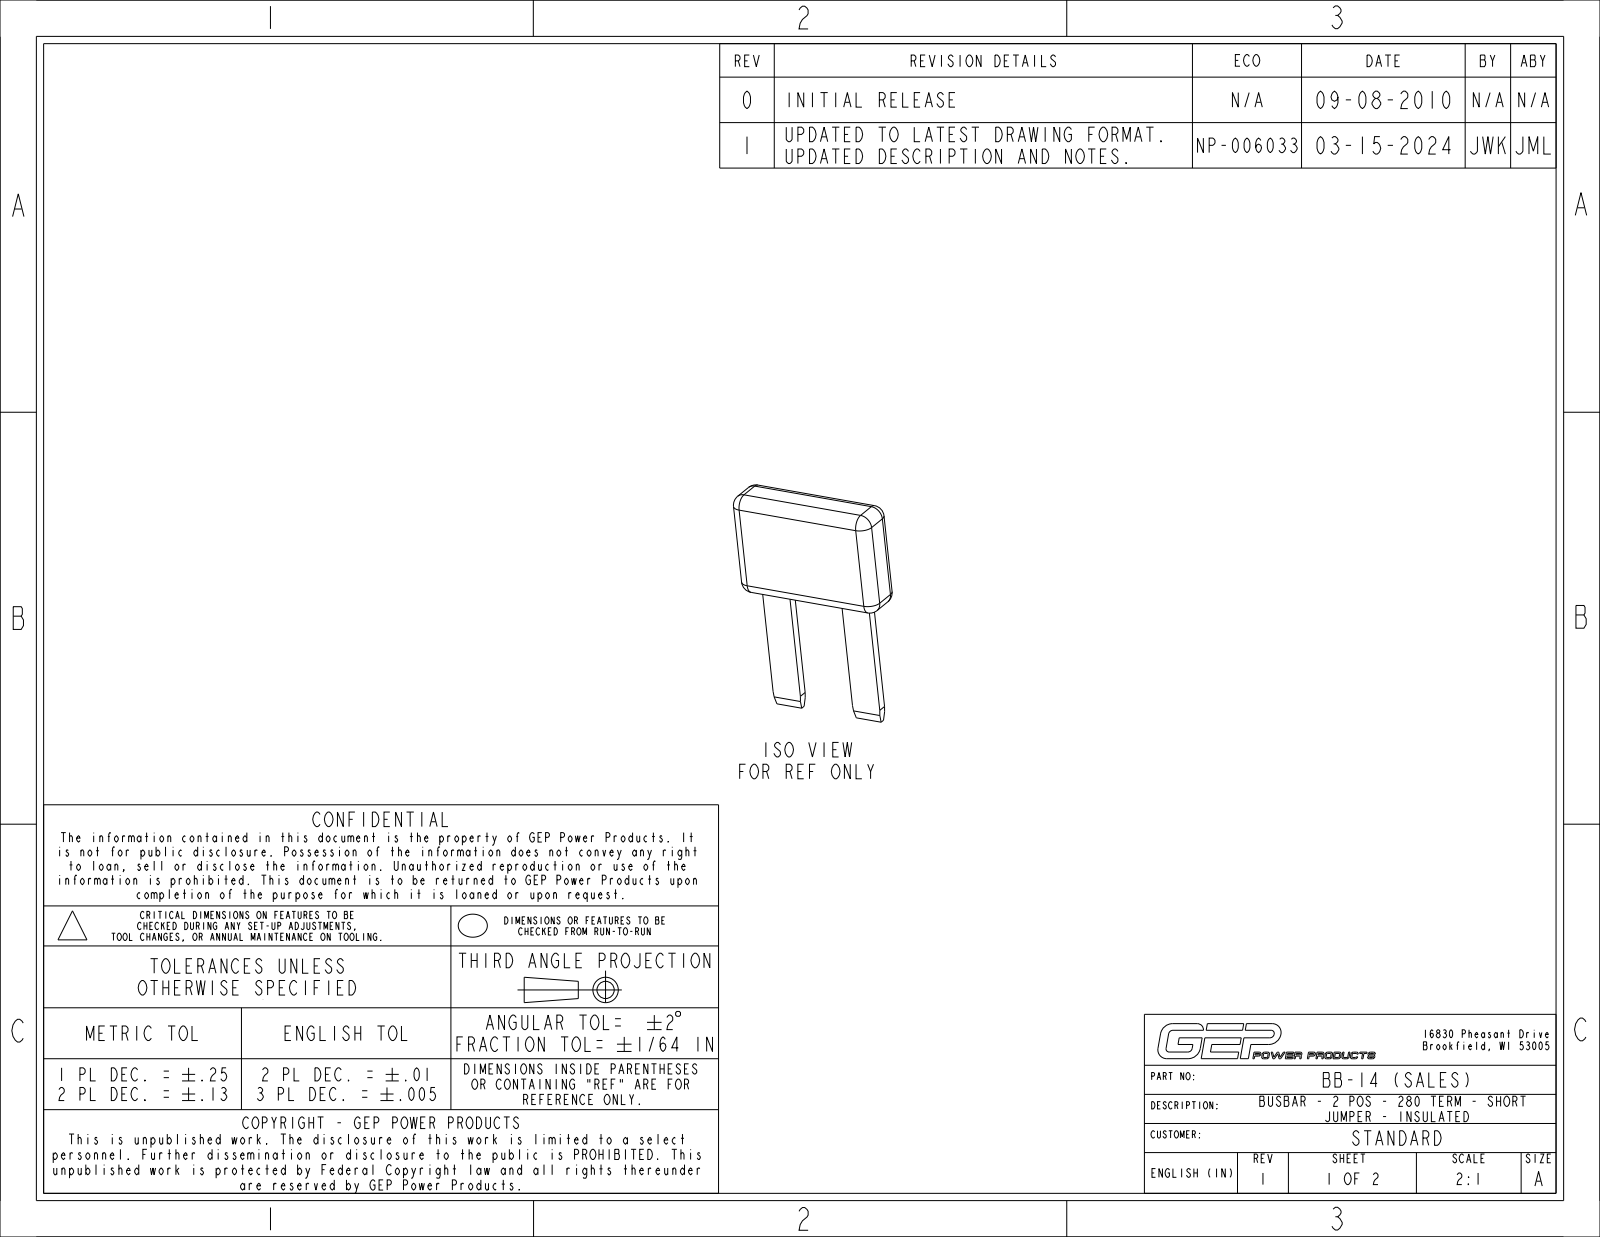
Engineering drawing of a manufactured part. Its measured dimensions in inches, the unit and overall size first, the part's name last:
Units: inches
Overall size (bounding box): 0.81 × 0.55 × 0.152
Partial cylindrical surfaces — rounded edges, fillets, slot ends (radius × count): R0.04 ×12
Main face-to-face distances: 0.032, 0.06, 0.06, 0.092, 0.152, 0.092, 0.31, 0.11, 0.32, 0.43
Volume: 0.033 in³ · Surface area: 1.427 in²
Bodies: 2 solids, 52 faces (32 planar, 12 cylindrical, 8 other)
Part name (STEP PRODUCT): BB-14_BUSBAR_NCF; BB-14_MOLD_NCF; BB-14_NCF_ASM; BB-14_SALES_NCF_ASM
STEP written by: CREO PARAMETRIC BY PTC INC, 2017110 (CONFIG_CONTROL_DESIGN)
